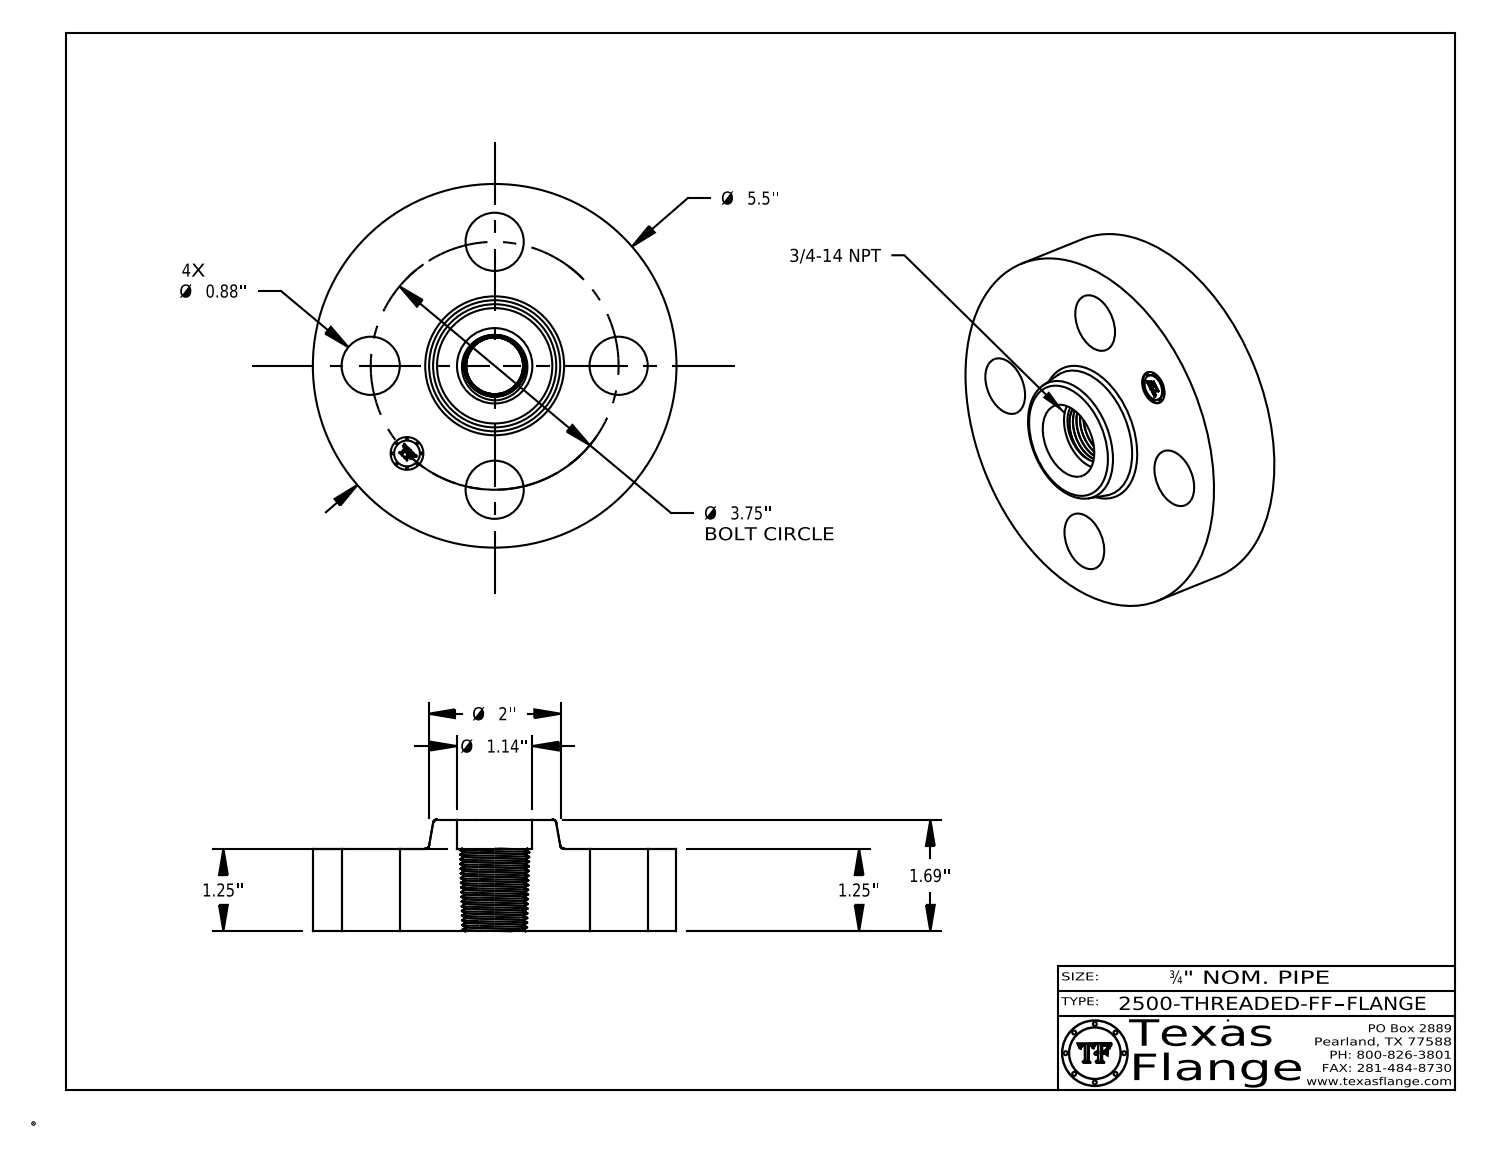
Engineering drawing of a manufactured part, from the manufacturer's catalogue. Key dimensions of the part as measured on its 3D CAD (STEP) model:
Part name (STEP PRODUCT): 2500-THREADED-FF
STEP written by: CATIA V5 STEP AP214 (AUTOMOTIVE_DESIGN)
Units: inches
Bodies: 1 solid, 590 faces (369 planar, 32 cylindrical, 189 other)
Overall size (bounding box): 5.5 × 5.5 × 1.69
Volume: 26.6 in³ · Surface area: 87.33 in²
Round holes (diameter × count): ⌀0.88 ×4, ⌀0.495 ×1, ⌀1.14 ×1
Round bosses / shafts (diameter × count): ⌀0.03 ×8, ⌀5.5 ×1, ⌀0.39 ×1
Main face-to-face distances: 1.25, 1.69, 0.44, 1.235, 0.015, 0.455, 0.148, 0.144, 0.027, 0.096
Hole centre spacings: 1.875, 2.652, 1.435, 3.465, 3.75
